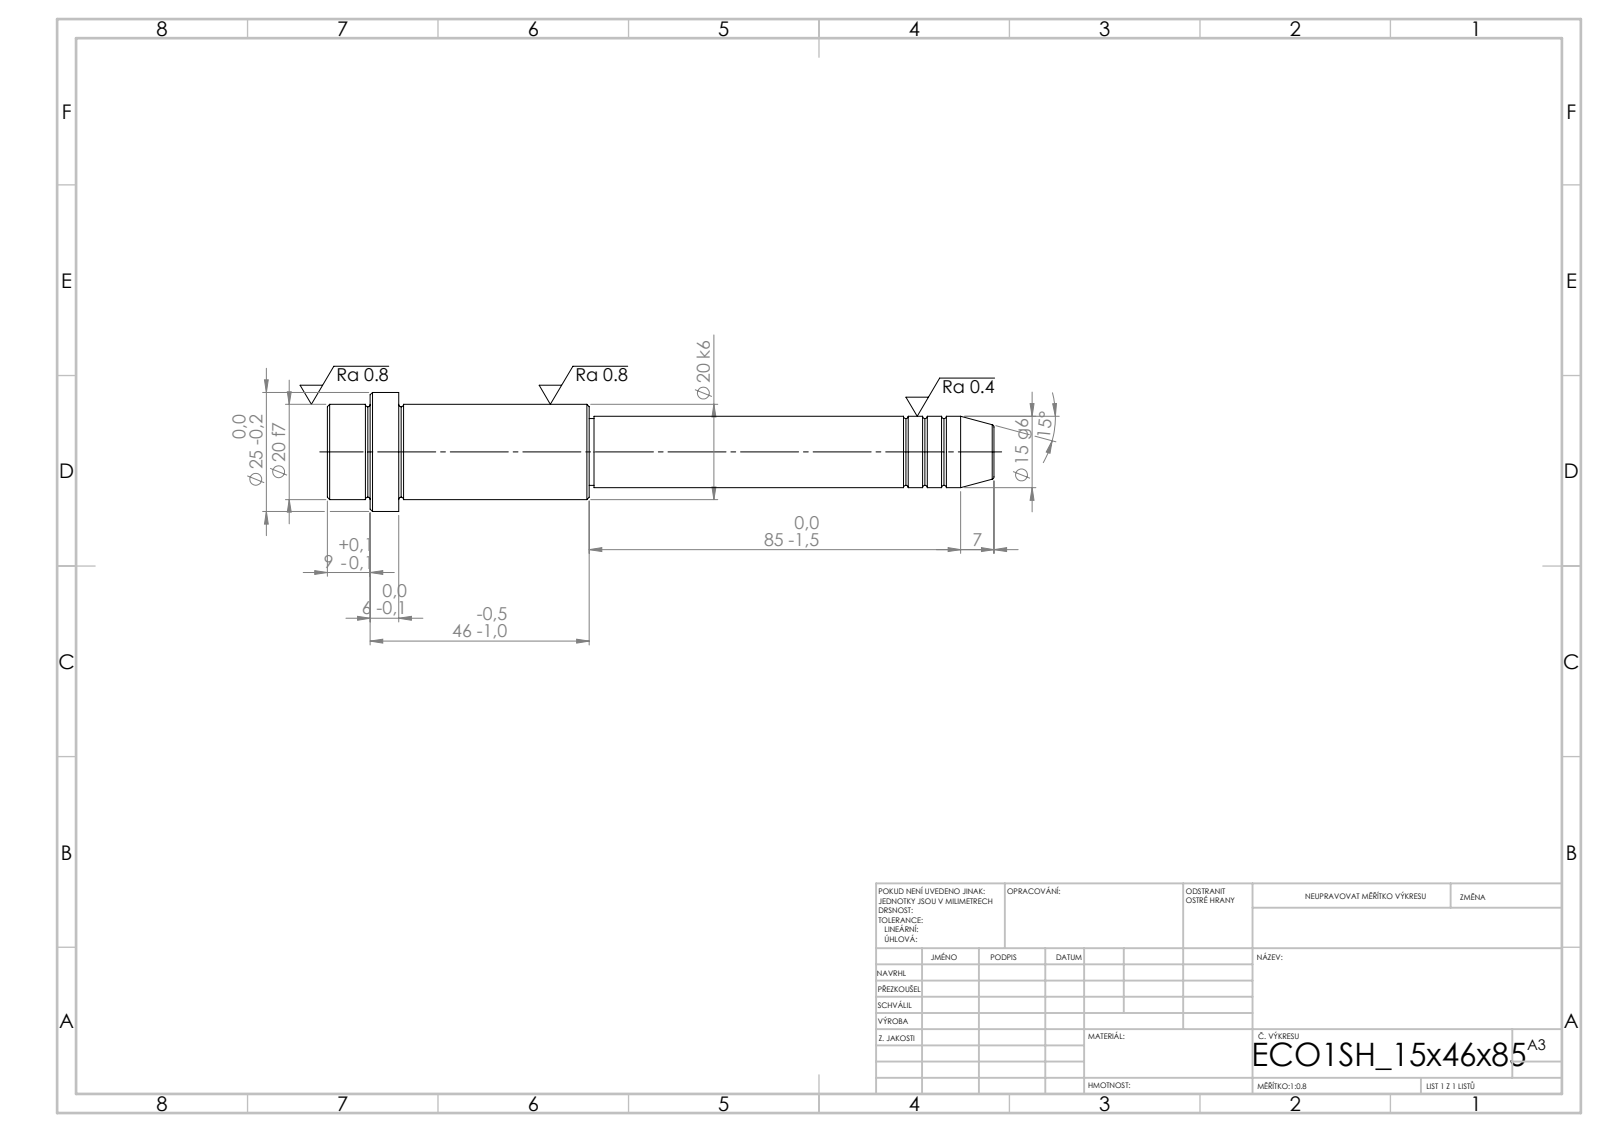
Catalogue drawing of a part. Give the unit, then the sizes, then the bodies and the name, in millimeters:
Units: millimetres
Overall size (bounding box): 140 × 25 × 25
Round bosses / shafts (diameter × count): ⌀25 ×1, ⌀20 ×1, ⌀15 ×1, ⌀14 ×1
Main face-to-face distances: 15, 6, 9, 40, 46, 55, 85, 125, 131, 140
Volume: 32 925 mm³ · Surface area: 8 543 mm²
Bodies: 1 solid, 52 faces (6 planar, 16 cylindrical, 30 other)
STEP written by: SolidWorks 2019 (CONFIG_CONTROL_DESIGN)
